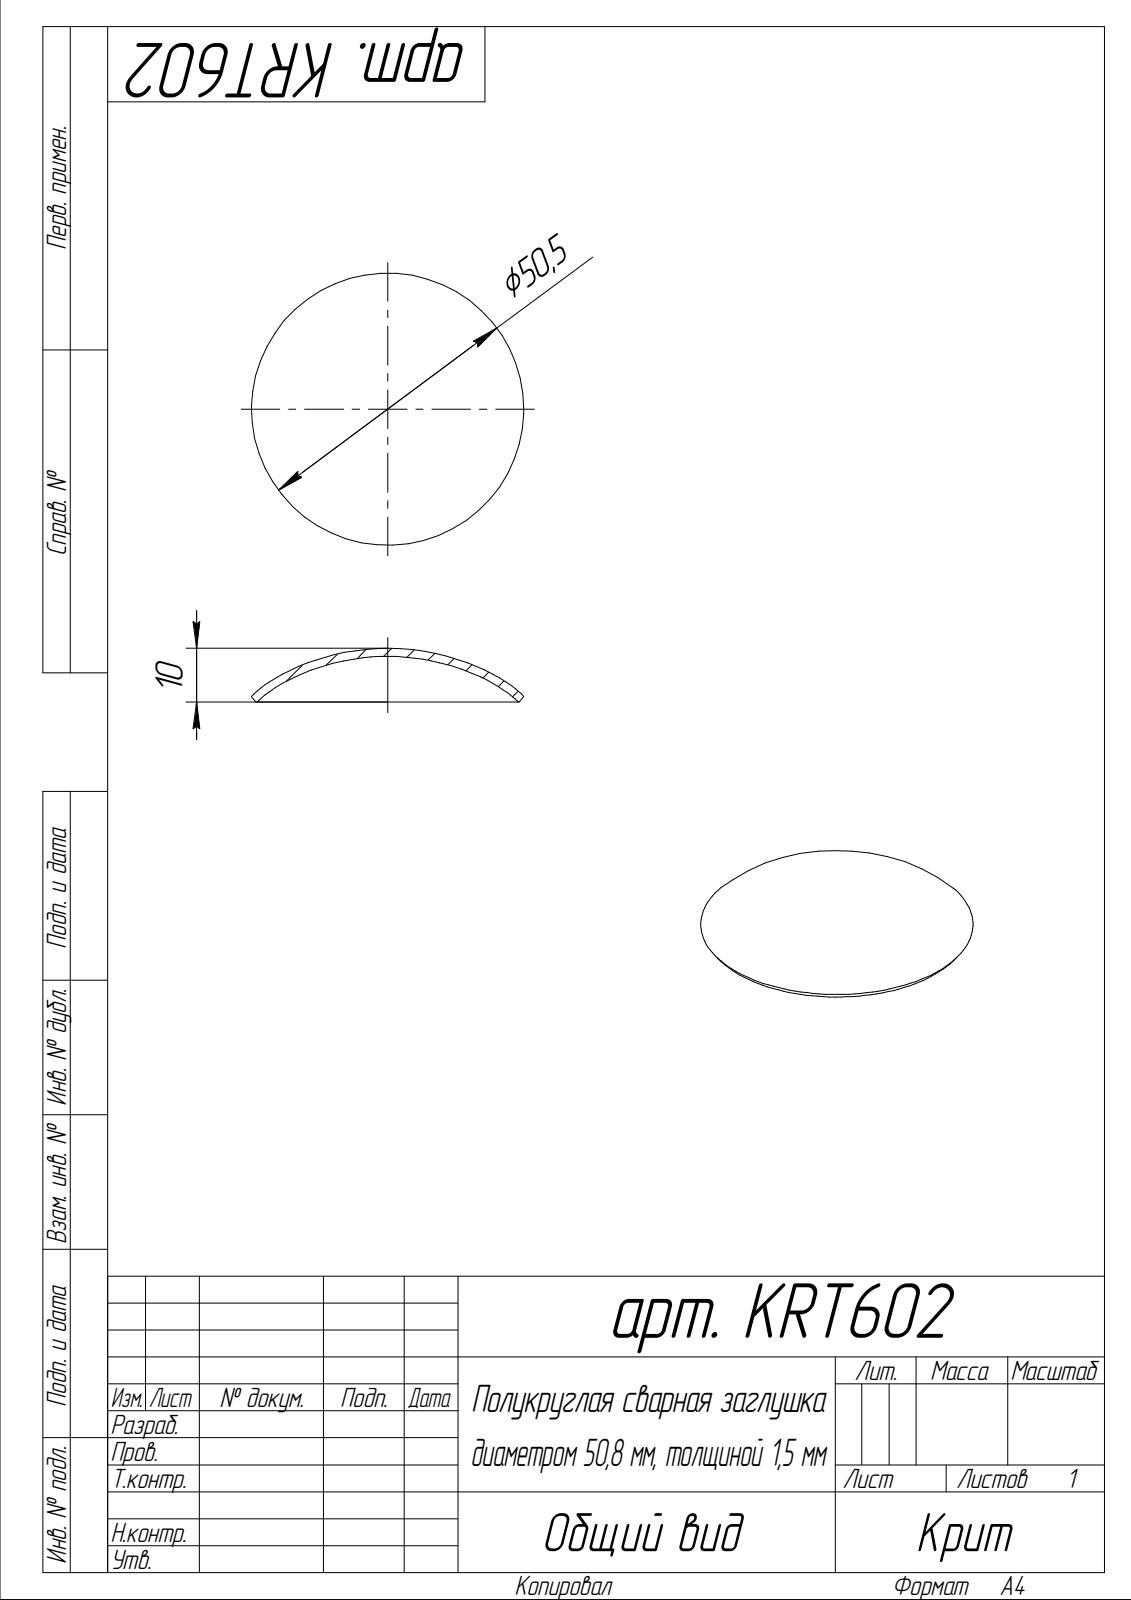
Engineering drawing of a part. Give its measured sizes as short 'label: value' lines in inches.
name: арт. KRT602
written by: SolidWorks 2014 (AUTOMOTIVE_DESIGN)
unit: in
bodies: 1 solid, 7 faces (1 planar, 0 cylindrical, 6 other)
size: 1.989 × 1.989 × 0.394
volume: 0.201 in³; area: 7.136 in²
